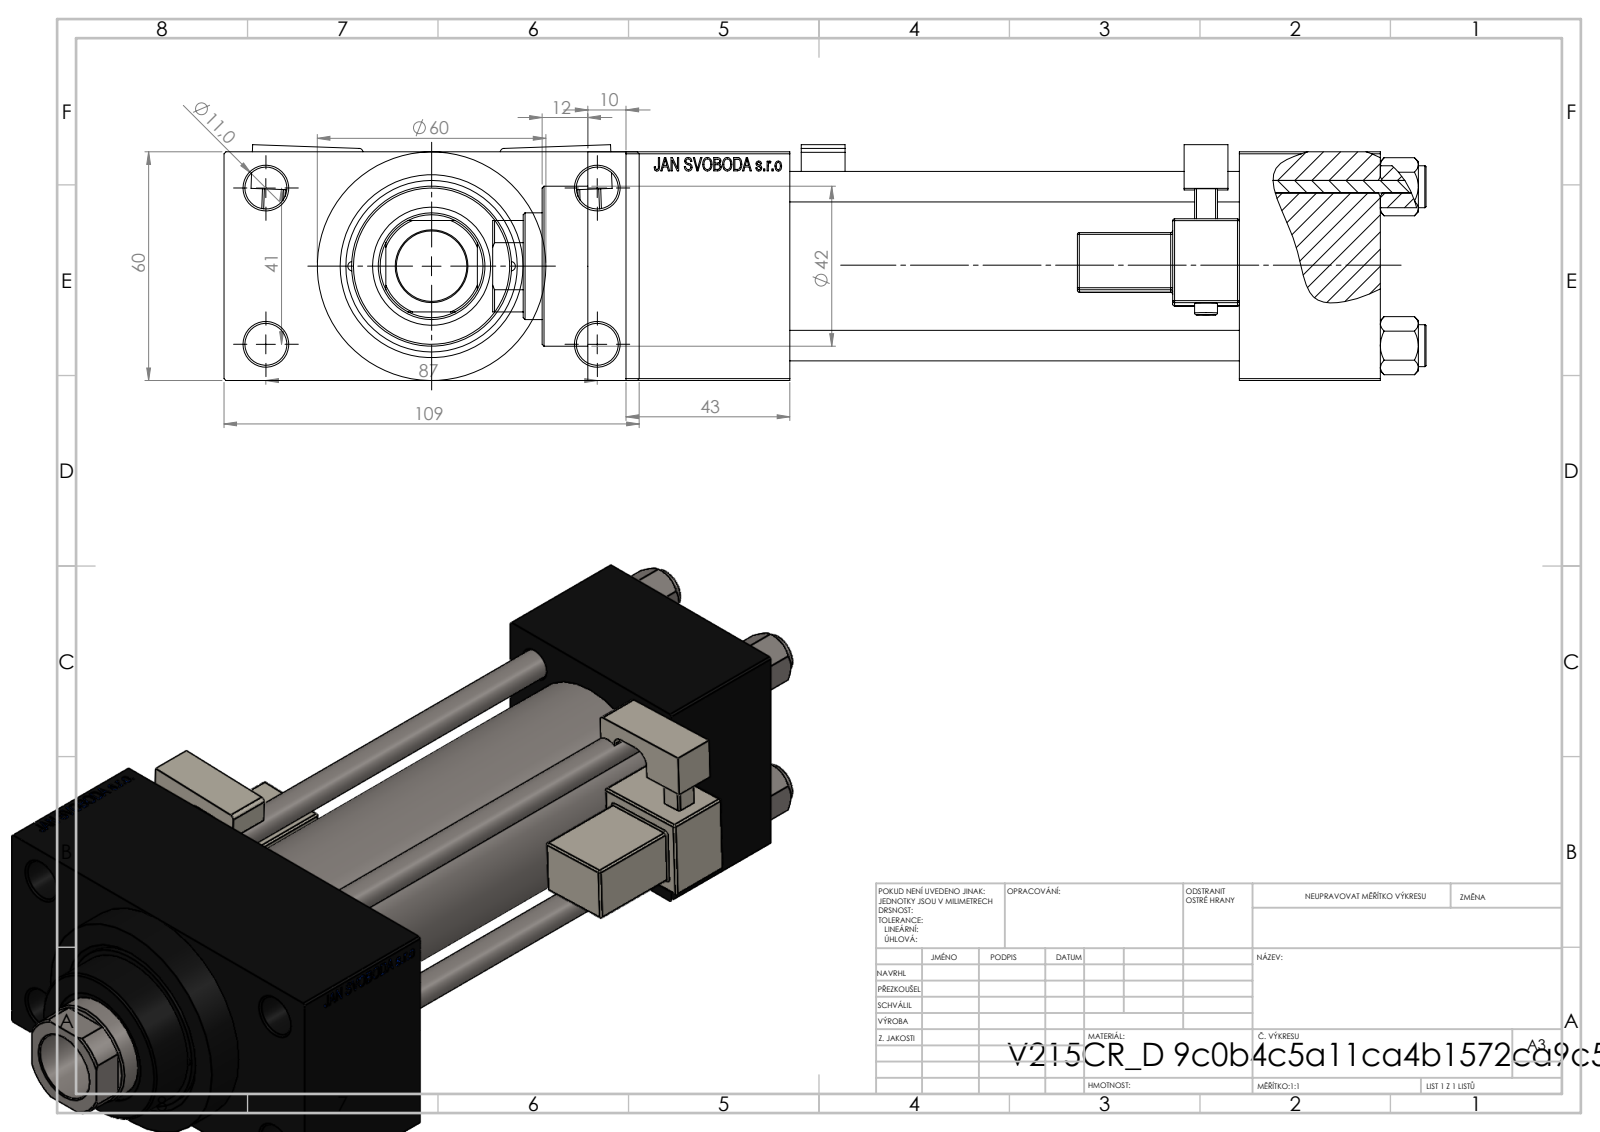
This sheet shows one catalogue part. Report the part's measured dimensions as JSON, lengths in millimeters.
{"part_name": "V215CR_D_Body; V215_VC_A; NUT_M5_D; V215CR_VCP_D (+2 more)", "step_written_by": "SolidWorks 2019 (CONFIG_CONTROL_DESIGN)", "units": "millimeters", "bodies": {"solids": 13, "faces": 1268, "planar": 560, "cylindrical": 152, "other": 556}, "overall_size": [245, 109, 61.9], "volume_mm3": 642826, "surface_area_mm2": 168683, "round_holes": [[8, 4], [11, 4], [2.5, 2], [7, 2], [16.66, 2], [24, 2], [18.5, 1], [28, 1], [31, 1], [40, 1], [45, 1]], "round_bosses_or_shafts": [[11, 4], [6, 2], [60, 1], [46, 1], [42, 1]], "partial_cylinders_radius": [[0.5, 48], [1, 2], [2.5, 2], [4, 2], [13.5, 1]], "face_to_face_distances": [60, 118, 24.5, 84.5, 37, 155, 198, 161, 43, 109], "hole_center_spacings": [20.85, 22.65, 29.49, 30.62, 41.7, 46.53, 47.15, 48.09]}
